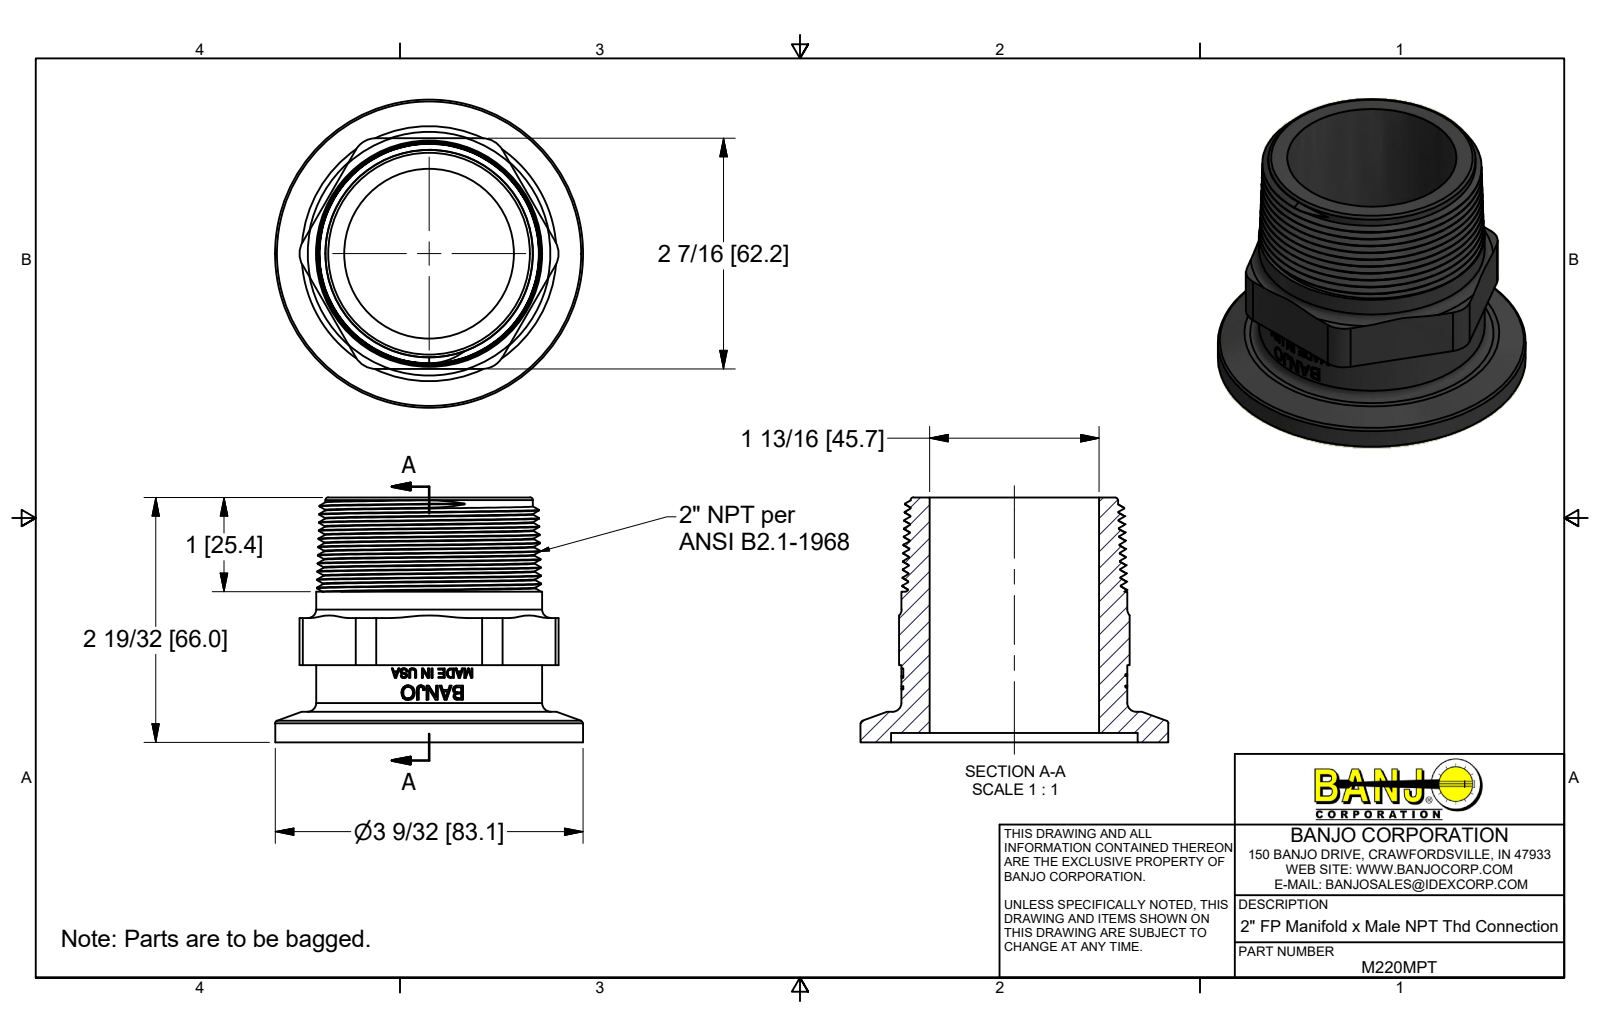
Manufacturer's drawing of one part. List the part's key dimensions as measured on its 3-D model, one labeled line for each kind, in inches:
Part name (STEP PRODUCT): M220MPT; M220MPTU
STEP written by: Autodesk Inventor 2018 (AUTOMOTIVE_DESIGN)
Units: inches
Bodies: 1 solid, 345 faces (145 planar, 42 cylindrical, 158 other)
Overall size (bounding box): 37.996 × 3.27 × 3.27
Volume: 5.918 in³ · Surface area: 304.7 in²
Round holes (diameter × count): ⌀1.8 ×1, ⌀2.62 ×1
Round bosses / shafts (diameter × count): ⌀3.27 ×1, ⌀2.4 ×1
Partial cylindrical surfaces — rounded edges, fillets, slot ends (radius × count): R0.25 ×6, R0.614 ×1, R1.18 ×1
Main face-to-face distances: 0.1, 2.45, 2.6, 2.5, 0.82, 0.72, 1.78, 2.45, 0.324, 0.224
